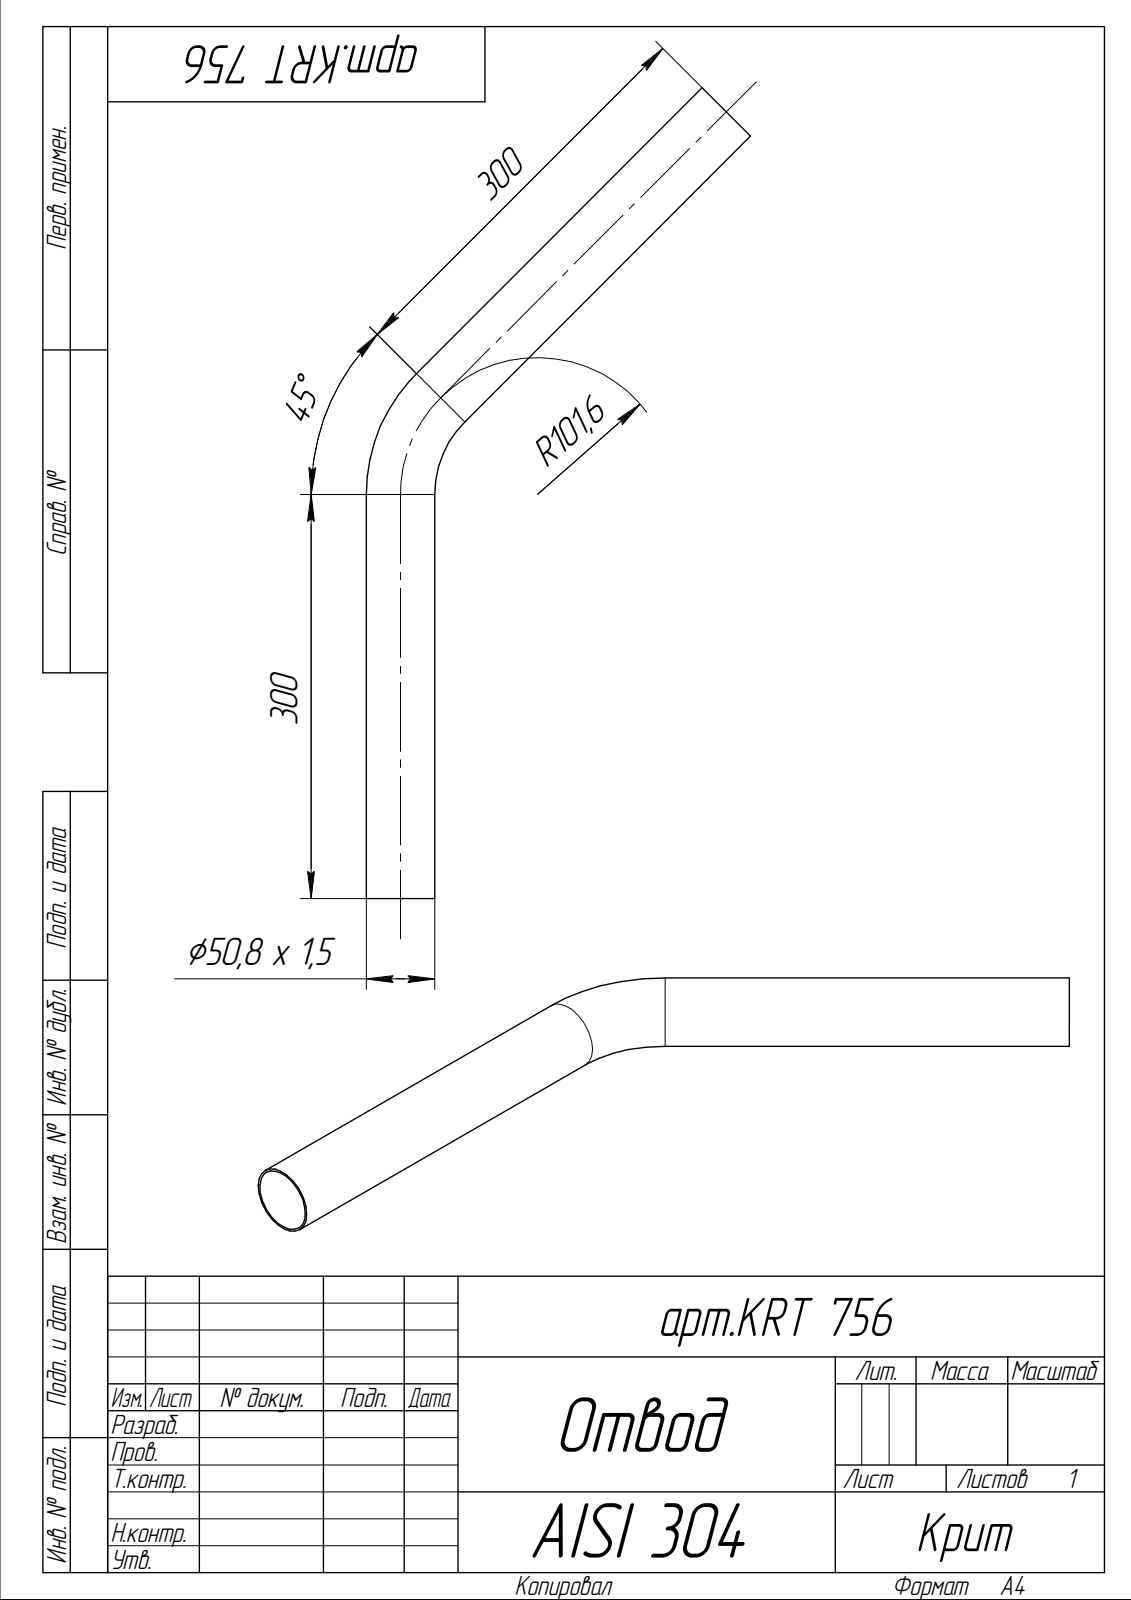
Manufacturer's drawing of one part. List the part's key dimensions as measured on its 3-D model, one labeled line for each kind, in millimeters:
Part name (STEP PRODUCT): Деталь
STEP written by: ASCON Math Kernel (AUTOMOTIVE_DESIGN)
Units: millimetres
Bodies: 1 solid, 8 faces (2 planar, 4 cylindrical, 2 other)
Overall size (bounding box): 601.93 × 285.25 × 50.8
Volume: 157 931 mm³ · Surface area: 211 039 mm²
Round holes (diameter × count): ⌀47.8 ×2
Round bosses / shafts (diameter × count): ⌀50.8 ×2
